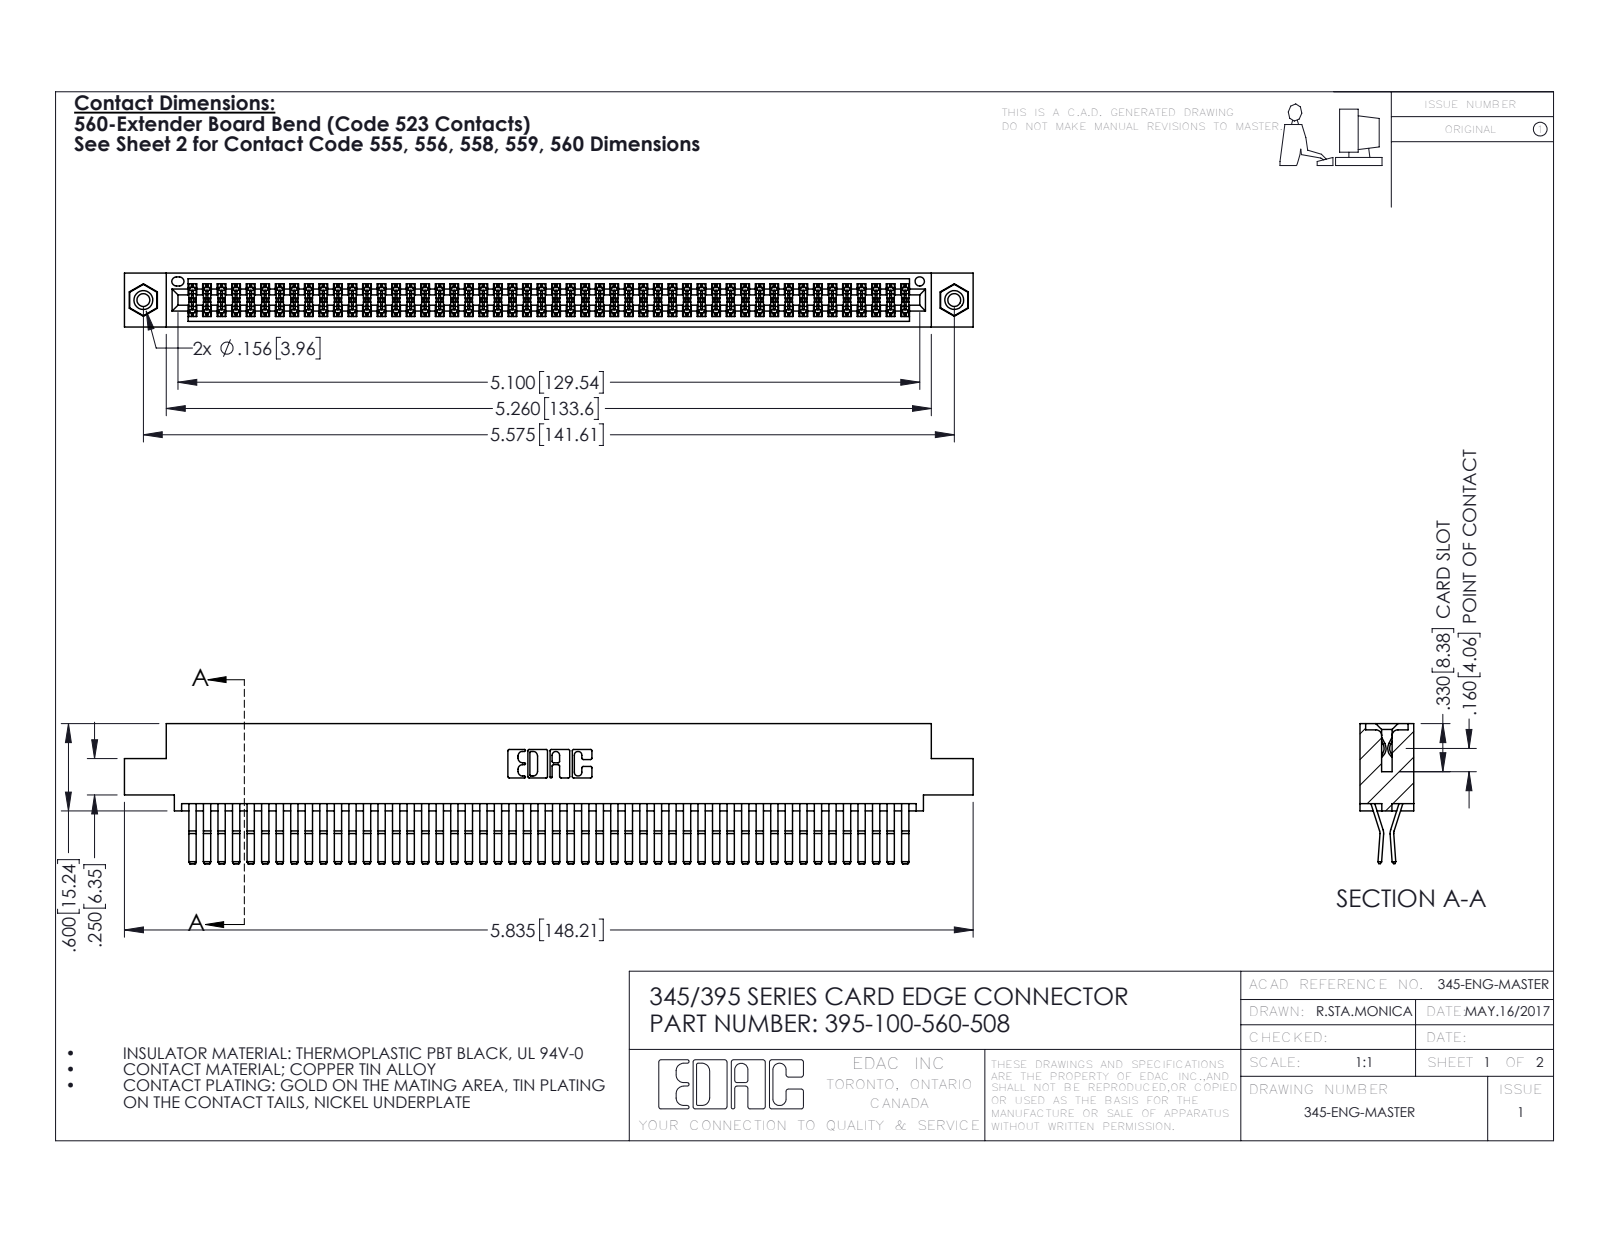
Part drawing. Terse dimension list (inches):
name: 395-100-560-508; 345-292-001_560 Tail; 345-250-001_345-250-003-102; 345 Part_0.110 Offset - 0.156 Dia-TI
written by: SolidWorks 2016 (CONFIG_CONTROL_DESIGN)
unit: in
bodies: 103 solids, 5390 faces (3416 planar, 1958 cylindrical, 16 other)
size: 5.835 × 0.962 × 0.37
volume: 0.918 in³; area: 37.49 in²
holes: 2× ⌀0.089, 2× ⌀0.125, 2× ⌀0.156, 1× ⌀0.064
bosses: 2× ⌀0.155
rounds: 151× R0.006, 22× R0.01, 6× R0.007, 6× R0.031, 3× R0.026, 2× R0.01, 2× R0.014, 2× R0.019
face distances: 0.025, 0.072, 0.298, 0.37, 0.2, 0.098, 0.272, 0.225, 0.175, 0.149
hole spacings: 0.27, 5.339, 5.575
